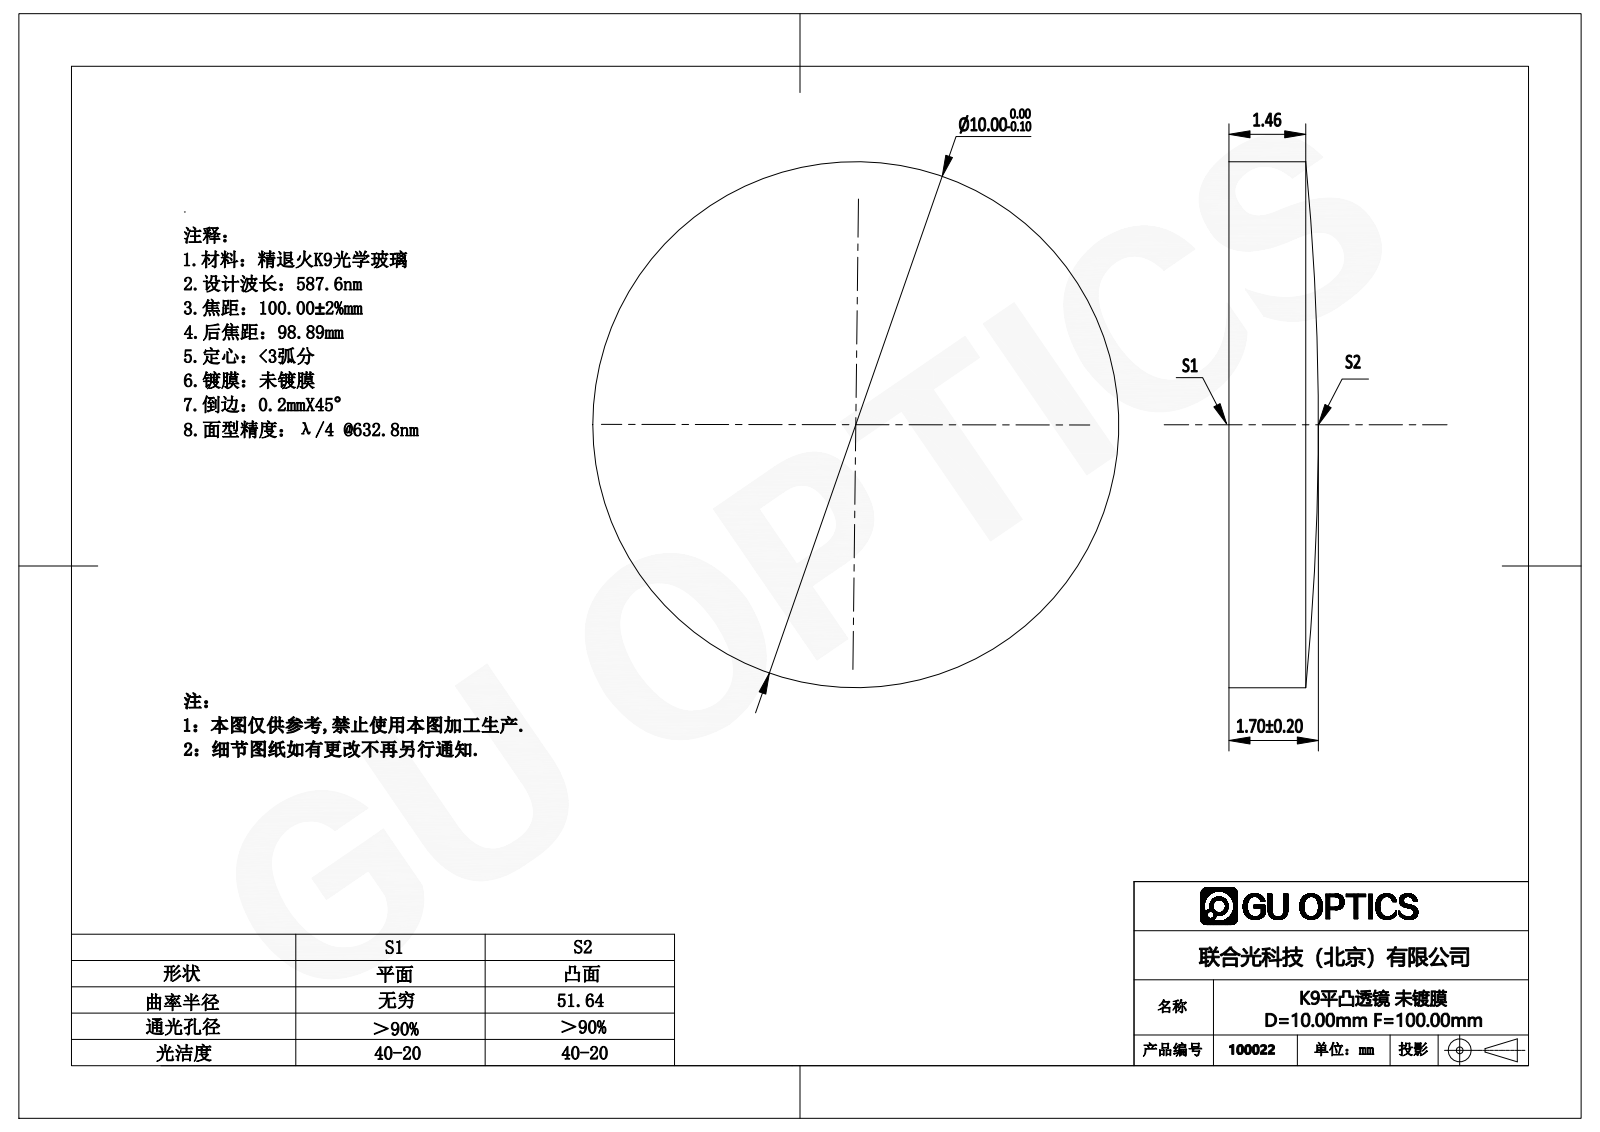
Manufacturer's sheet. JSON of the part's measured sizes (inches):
{"part_name": "100022", "step_written_by": "SolidWorks 2016 (AUTOMOTIVE_DESIGN)", "units": "inches", "bodies": {"solids": 1, "faces": 5, "planar": 1, "cylindrical": 2, "other": 2}, "overall_size": [0.394, 0.394, 0.067], "volume_in3": 0.008, "surface_area_in2": 0.315, "round_bosses_or_shafts": [[0.394, 1]]}
